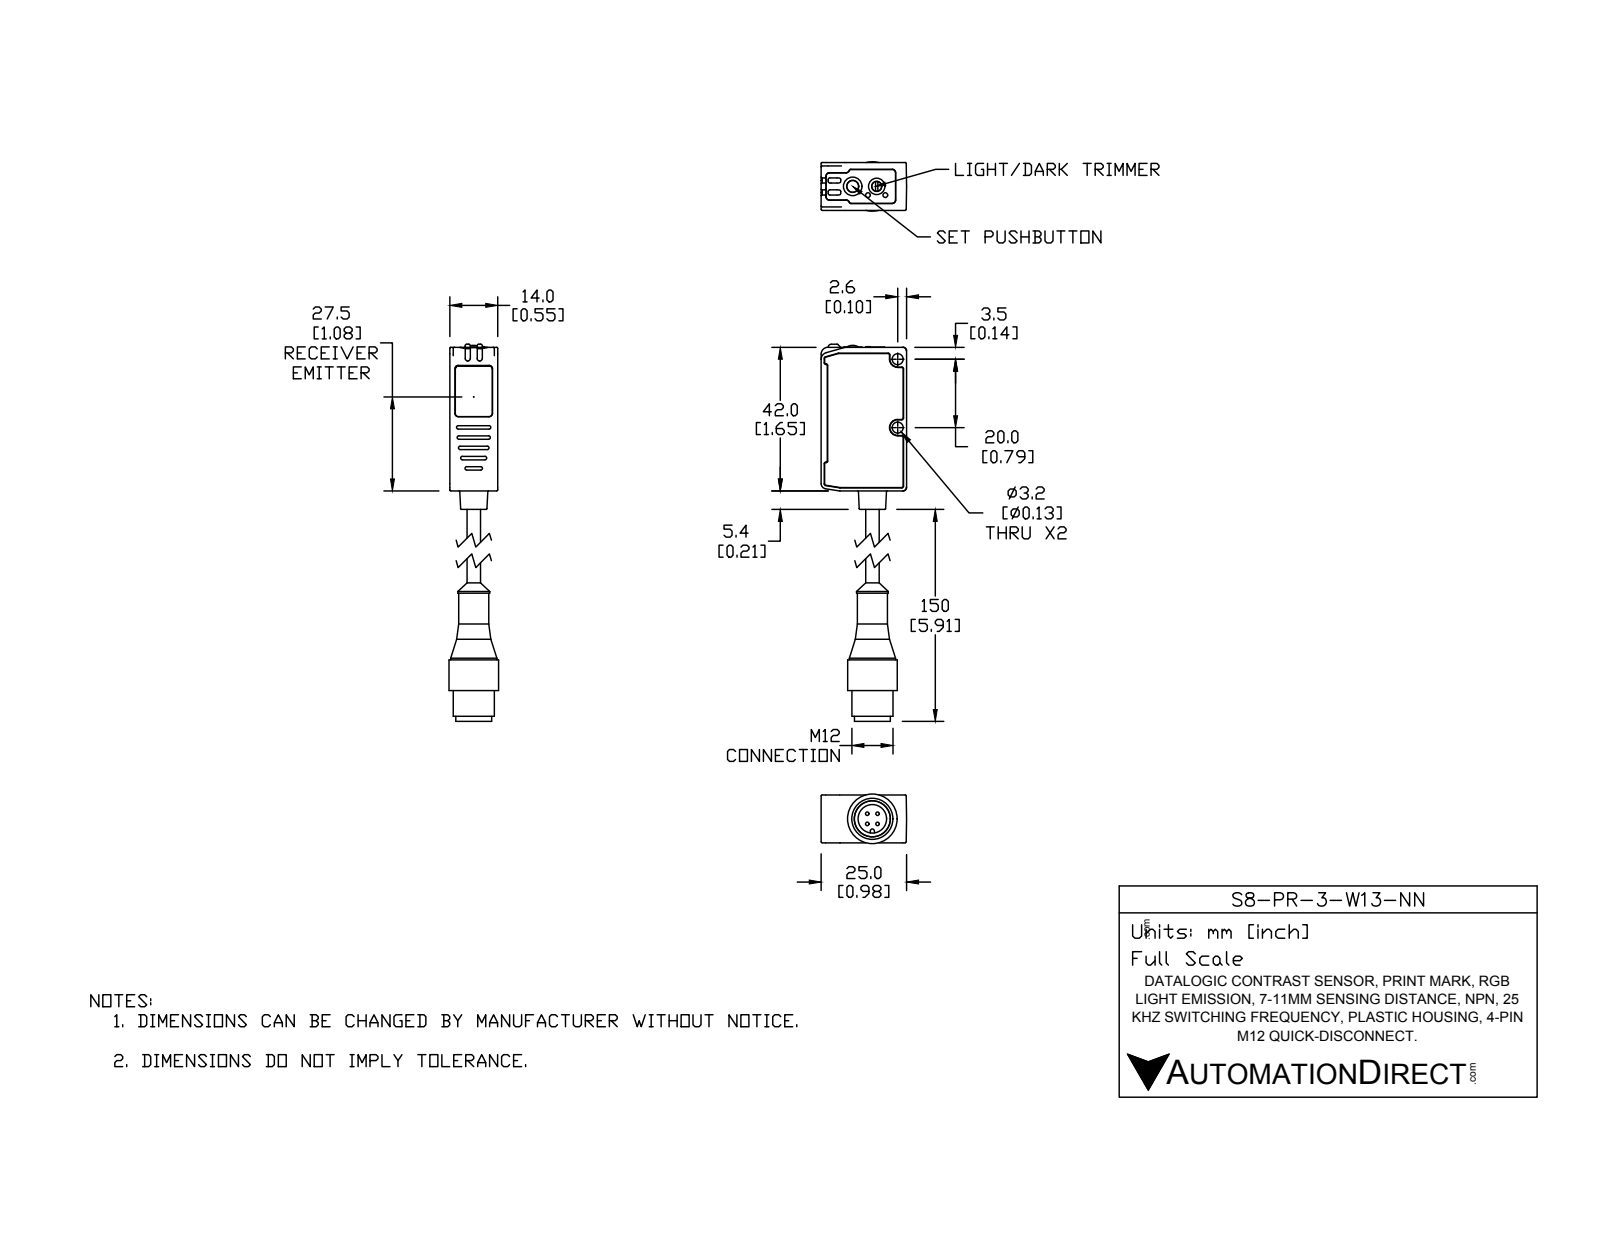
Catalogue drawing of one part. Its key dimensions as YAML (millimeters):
part_name: "S8-PR-3-W13-NN"
step_written_by: "SolidWorks 2016 (AUTOMOTIVE_DESIGN)"
units: millimeters
bodies: {solids: 13, faces: 453, planar: 132, cylindrical: 203, other: 118}
overall_size: [198.3, 25, 14.5]
volume: 18834
surface_area: 10015
round_holes:
  - {diameter: 3.2, count: 2}
  - {diameter: 1.4, count: 1}
  - {diameter: 2.95, count: 1}
  - {diameter: 3.5, count: 1}
  - {diameter: 8.3, count: 1}
  - {diameter: 10.55, count: 1}
round_bosses_or_shafts:
  - {diameter: 1, count: 4}
  - {diameter: 14.5, count: 1}
  - {diameter: 13.5, count: 1}
  - {diameter: 12, count: 1}
  - {diameter: 10.5, count: 1}
  - {diameter: 9.3, count: 1}
  - {diameter: 8.8, count: 1}
  - {diameter: 3.95, count: 1}
partial_cylinders:
  - {radius: 0.2, count: 41}
  - {radius: 0.5, count: 32}
  - {radius: 0.3, count: 18}
  - {radius: 1, count: 14}
  - {radius: 0.4, count: 13}
  - {radius: 0.7, count: 4}
  - {radius: 0.95, count: 4}
  - {radius: 2, count: 3}
face_to_face_distances: [14, 0.6, 178.8, 179.4, 137.4, 41.4, 42, 0.8, 1, 9]
hole_center_spacings: [1.25, 3.61, 4.58, 5.75, 7, 9.88, 20]
